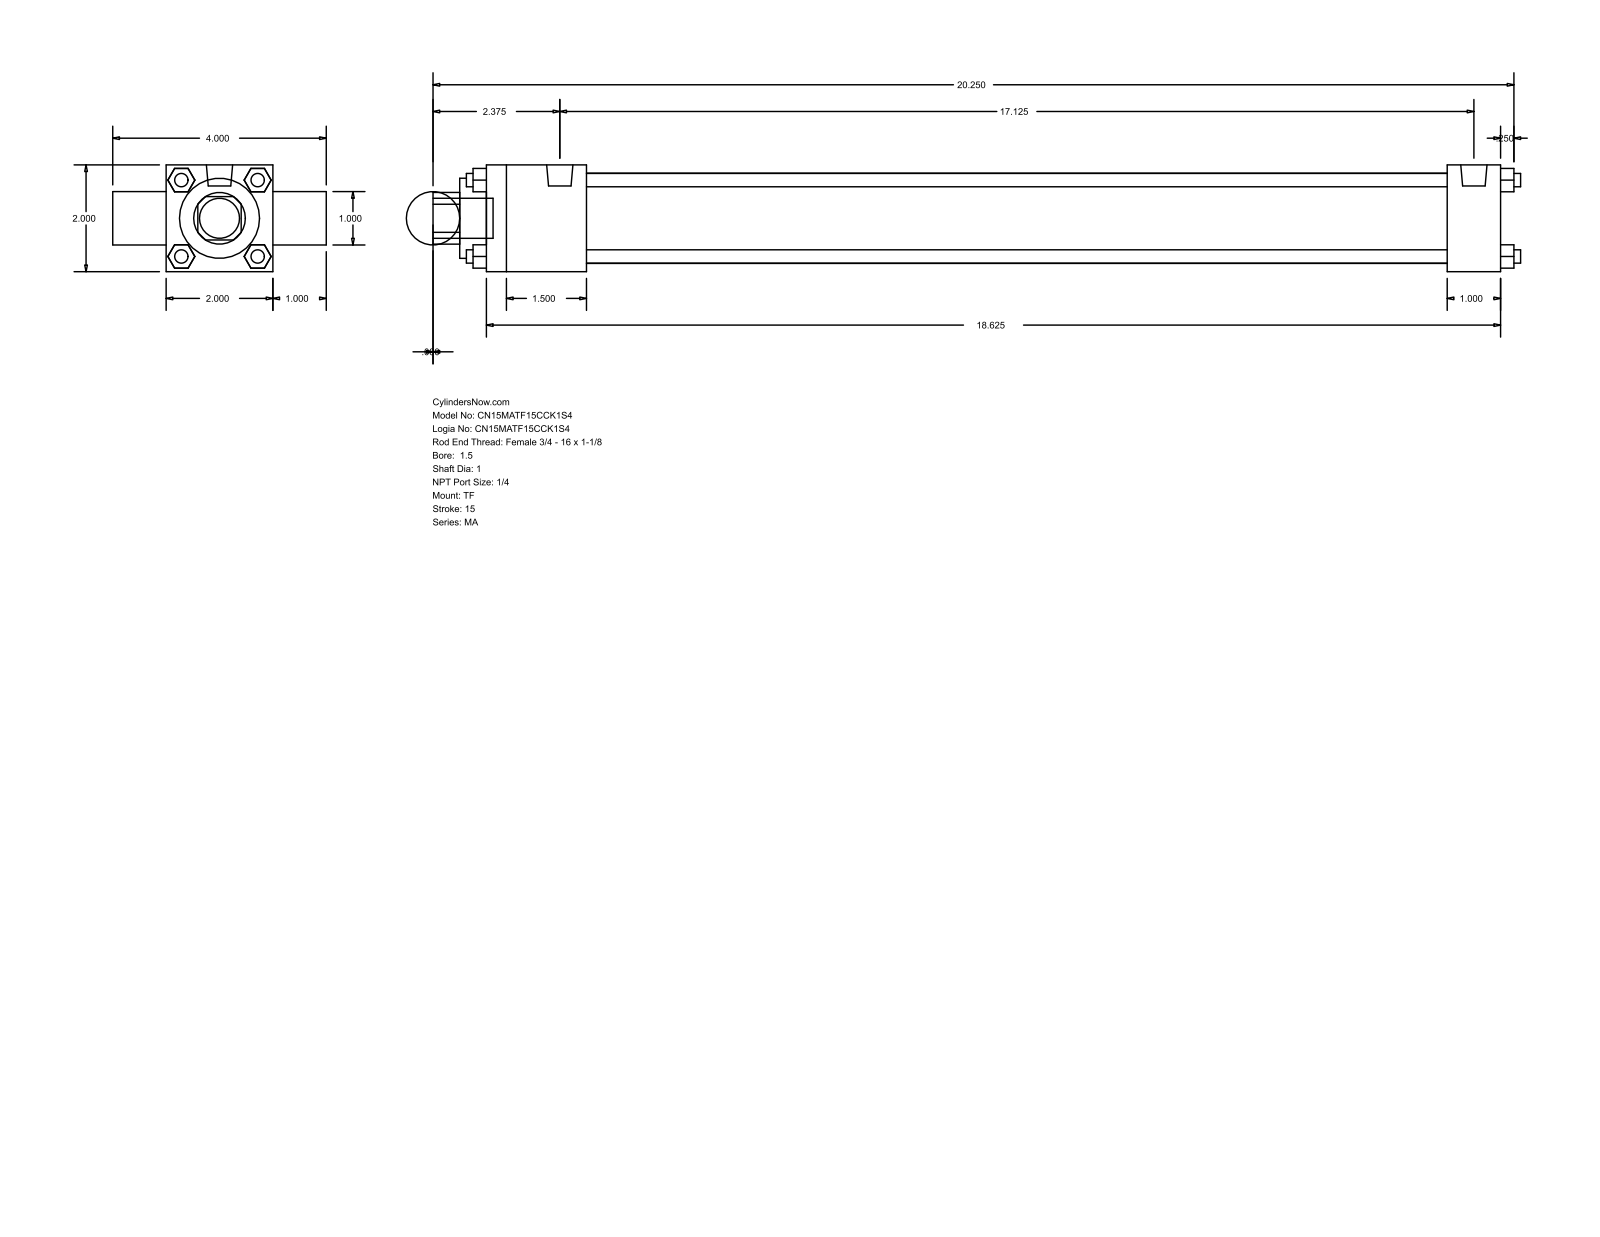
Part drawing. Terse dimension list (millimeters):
name: MA_TF__0150_1
written by: GSSL Pune (CONFIG_CONTROL_DESIGN)
unit: mm
bodies: 0 solids, 120 faces (92 planar, 28 cylindrical, 0 other)
size: 517.52 × 101.6 × 50.8
holes: 2× ⌀25.4, 1× ⌀38.1, 1× ⌀42.93
bosses: 4× ⌀6.35, 3× ⌀7.94, 2× ⌀12.49, 1× ⌀19.05
rounds: 1× R12.29
face distances: 50.8, 25.4, 482.6, 76.2, 6.35, 47.63, 457.2, 409.57, 434.97, 495.3
